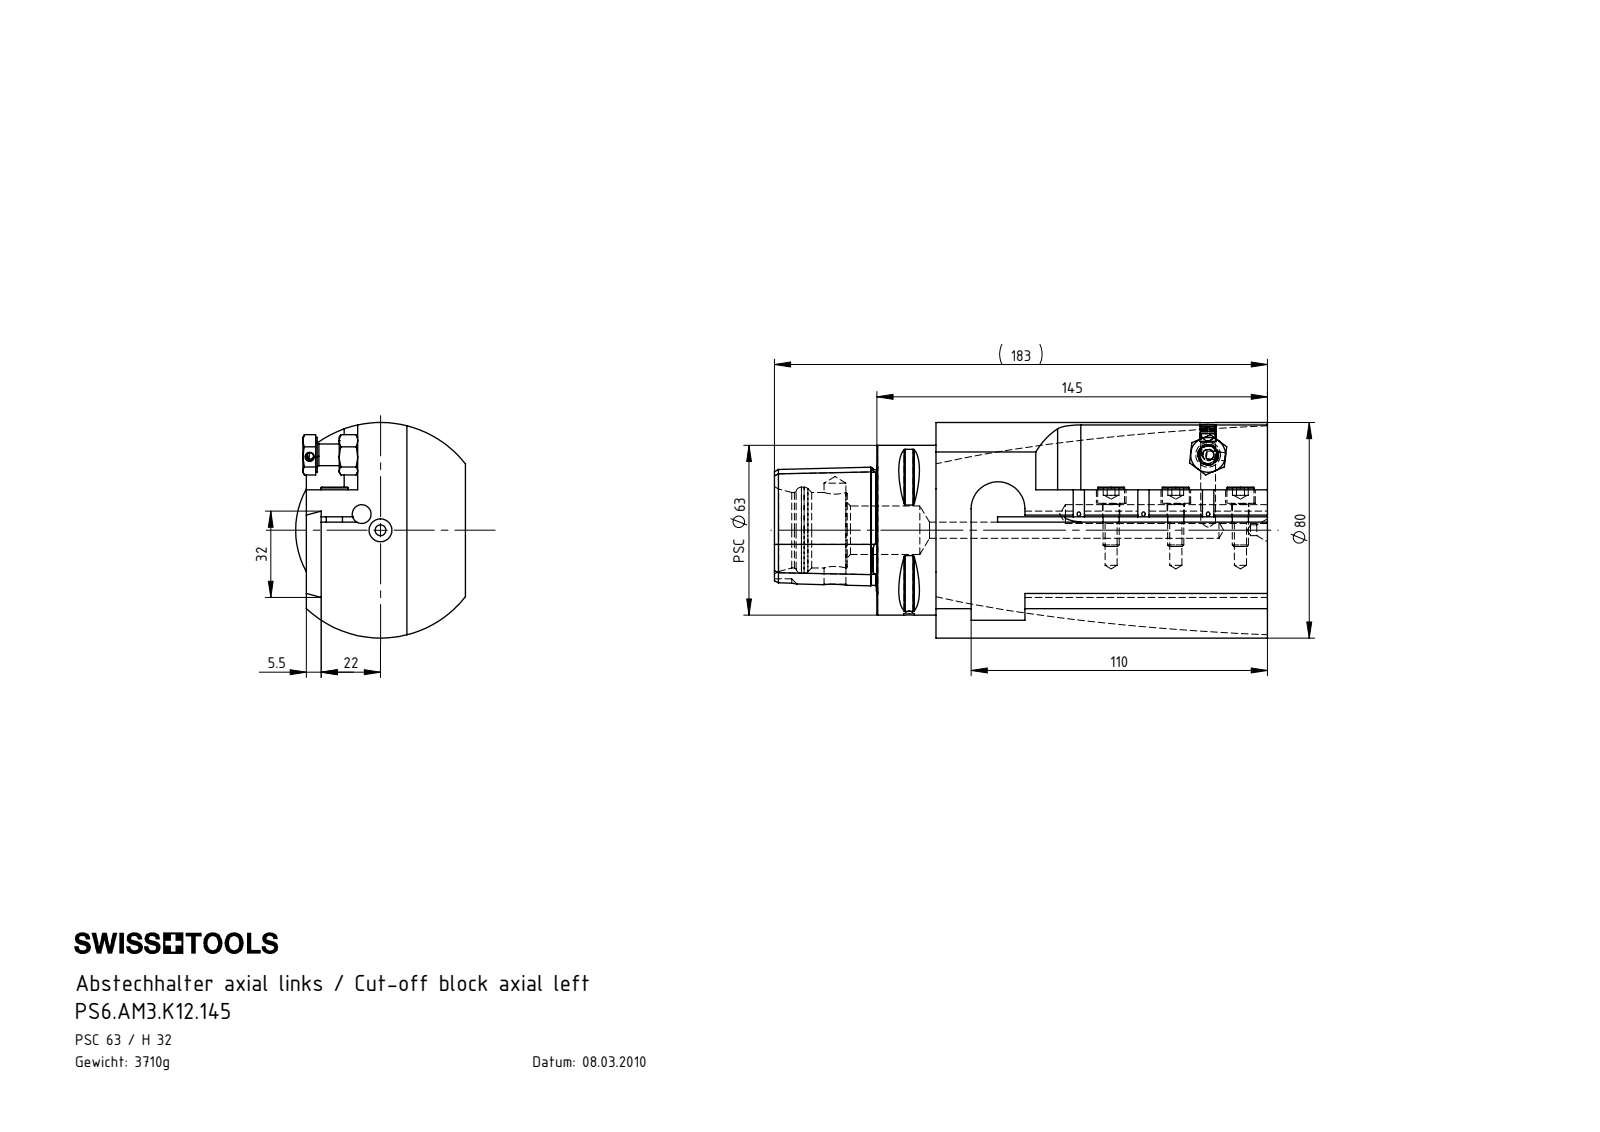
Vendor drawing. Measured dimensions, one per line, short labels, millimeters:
name: KVT_MB_600_060; PS6.AM3.K12.145; ISO 4035 - M8_PreviewCfg; AM3-ER1.001.020_PreviewCfg (+2 more)
written by: SolidWorks 2017 (AUTOMOTIVE_DESIGN)
unit: mm
bodies: 8 solids, 388 faces (122 planar, 91 cylindrical, 175 other)
size: 183 × 80 × 64.19
volume: 479 123 mm³; area: 63 703 mm²
holes: 4× ⌀6.4, 3× ⌀4, 3× ⌀4.5, 3× ⌀11, 2× ⌀7, 1× ⌀3, 1× ⌀5, 1× ⌀6, 1× ⌀8.1, 1× ⌀18, 1× ⌀28, 1× ⌀32
bosses: 4× ⌀6, 3× ⌀10, 1× ⌀63, 1× ⌀13, 1× ⌀8
rounds: 8× R0.5, 3× R2.1, 1× R6, 1× R10, 1× R40, 1× R77.5
face distances: 13.5, 19, 5.5, 145, 12, 22, 123, 2, 10, 24
hole spacings: 20.81, 24, 9.22, 27.5, 39.81, 48, 76.9, 100.45
